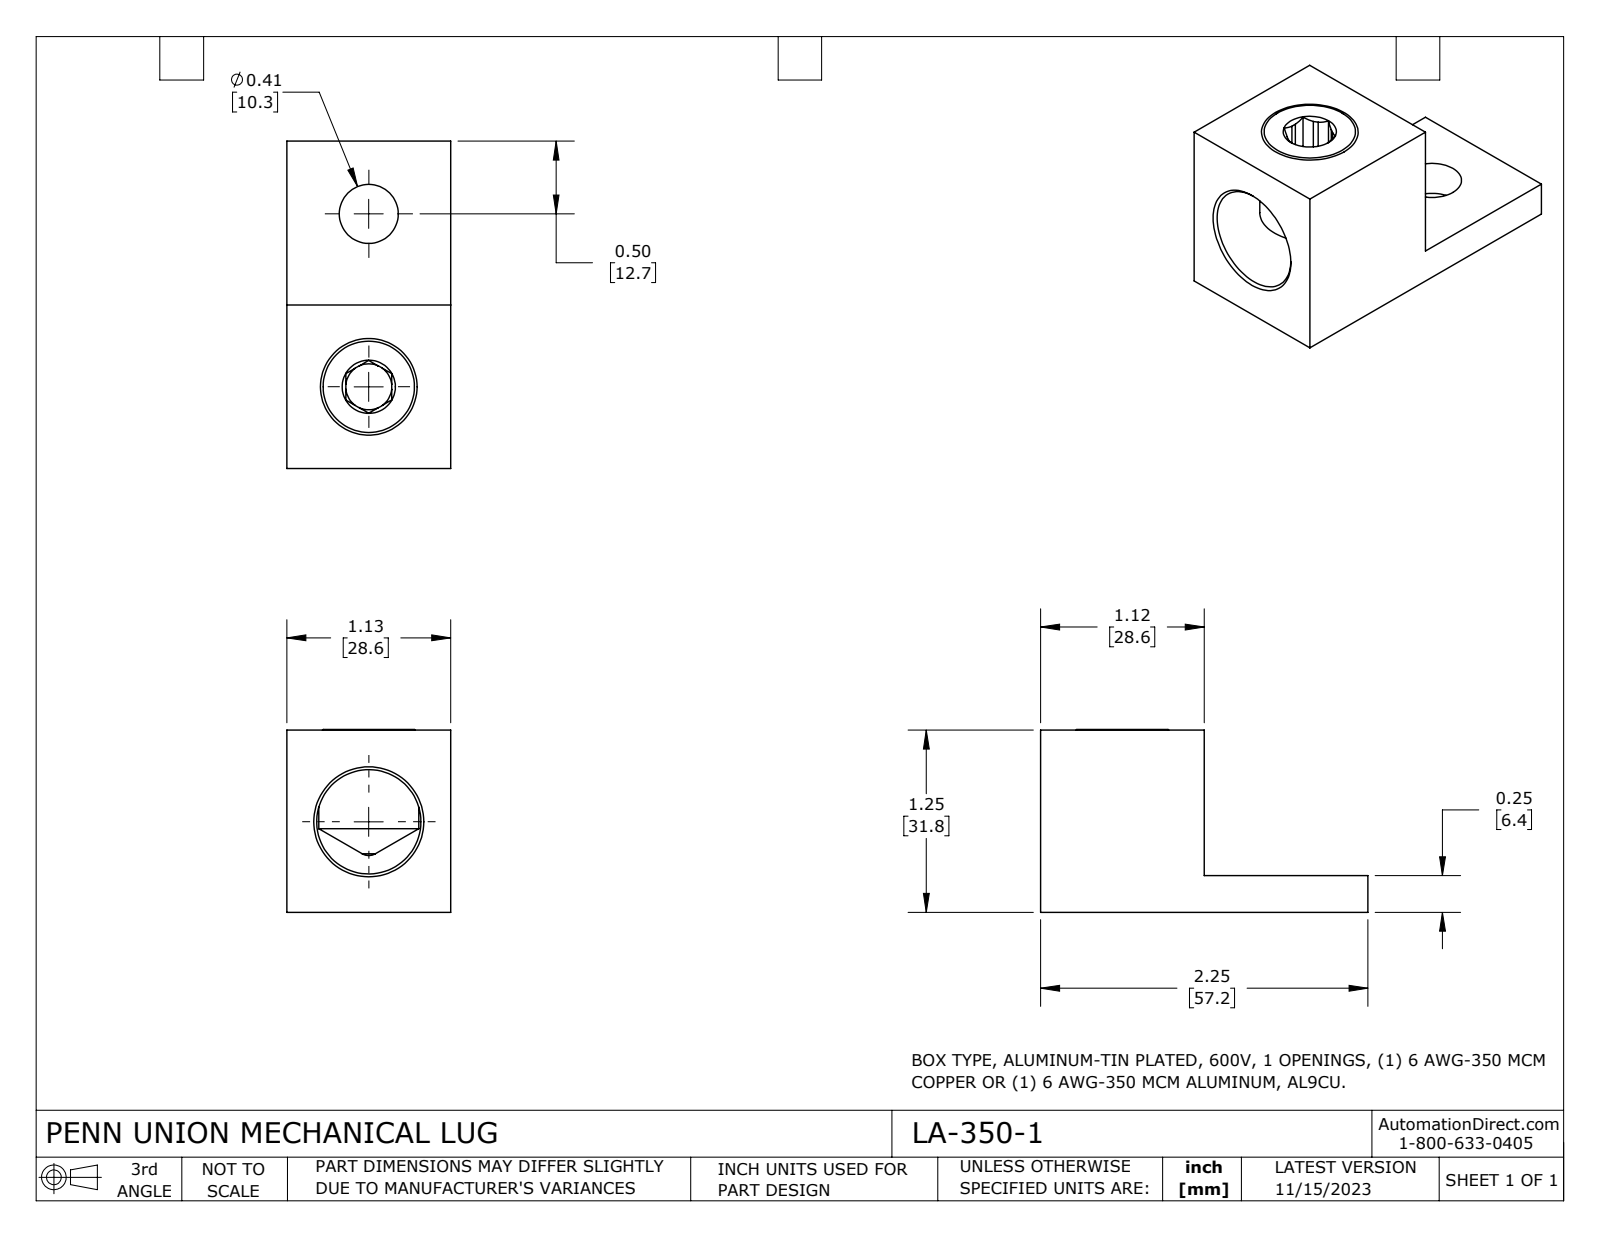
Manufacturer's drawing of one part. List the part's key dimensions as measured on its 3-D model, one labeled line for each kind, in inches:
Part name (STEP PRODUCT): LA-350-1
STEP written by: SolidWorks 2023 (CONFIG_CONTROL_DESIGN)
Units: inches
Bodies: 2 solids, 50 faces (27 planar, 10 cylindrical, 13 other)
Overall size (bounding box): 2.25 × 1.256 × 1.126
Volume: 1.556 in³ · Surface area: 15.79 in²
Round holes (diameter × count): ⌀0.316 ×1, ⌀0.406 ×1, ⌀0.625 ×1, ⌀0.717 ×1
Round bosses / shafts (diameter × count): ⌀0.687 ×1
Main face-to-face distances: 1.126, 0.252, 1.252, 1, 1.124, 2.25, 1.256, 1.004, 0.314, 0.406
Hole centre spacings: 1.188
